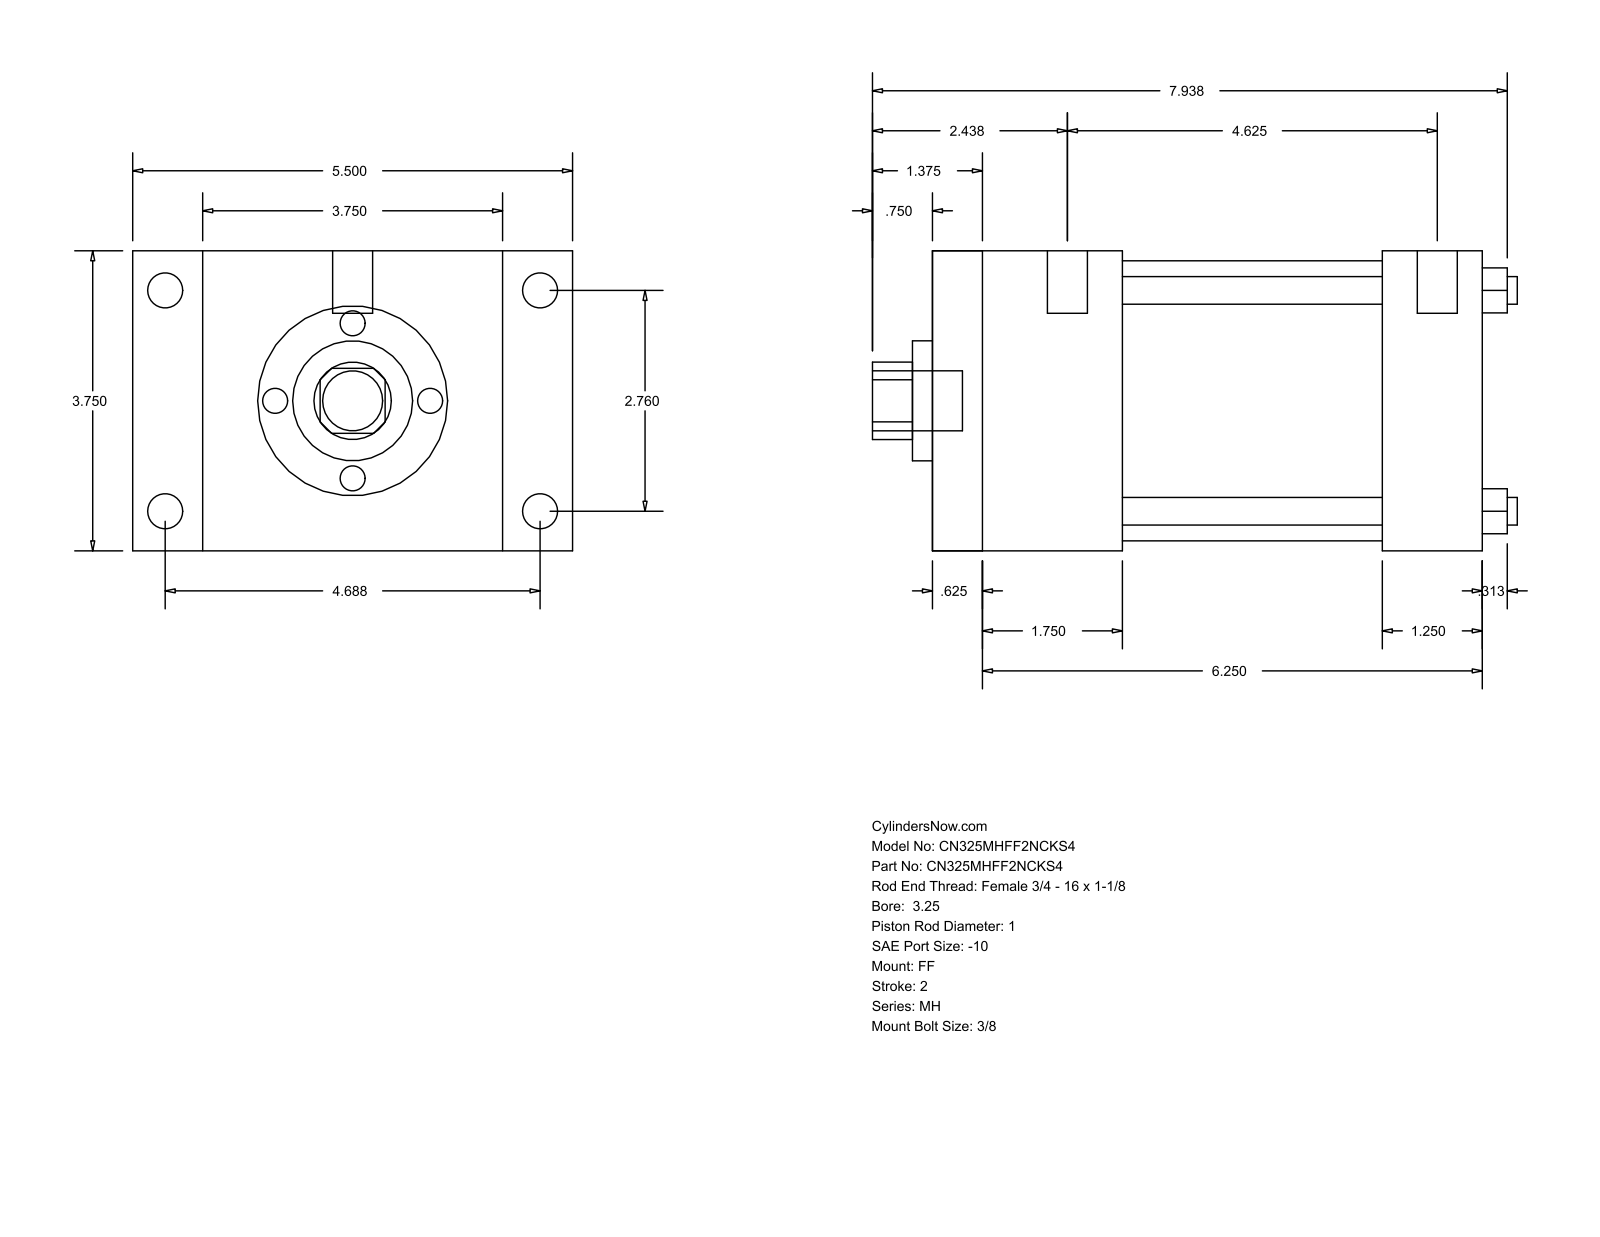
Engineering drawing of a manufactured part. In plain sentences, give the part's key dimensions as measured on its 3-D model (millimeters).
The part is named "MH_FF__0325_1". Its 3-D file was written by "GSSL Pune (CONFIG_CONTROL_DESIGN)". It is 0 solids with 92 faces: 64 planar, 28 cylindrical and 0 other. Overall it measures 204.79 by 139.7 by 95.25 millimeters. Round holes: 4 of diameter 8.76, 1 of diameter 25.4, 1 of diameter 38.1, 1 of diameter 88.9. Round bosses or shafts: 4 of diameter 11.13, 4 of diameter 5.56, 2 of diameter 12.7, 1 of diameter 19.05. Partial cylindrical surfaces (rounded edges, fillets, slot ends): 1 of radius 12.29. The main face-to-face distances are 95.24, 174.63, 15.87, 158.76, 22.23, 117.47, 142.88, 127.01, 31.75, 60.33. The hole center spacings are 49.57, 70.1, 99.14.
